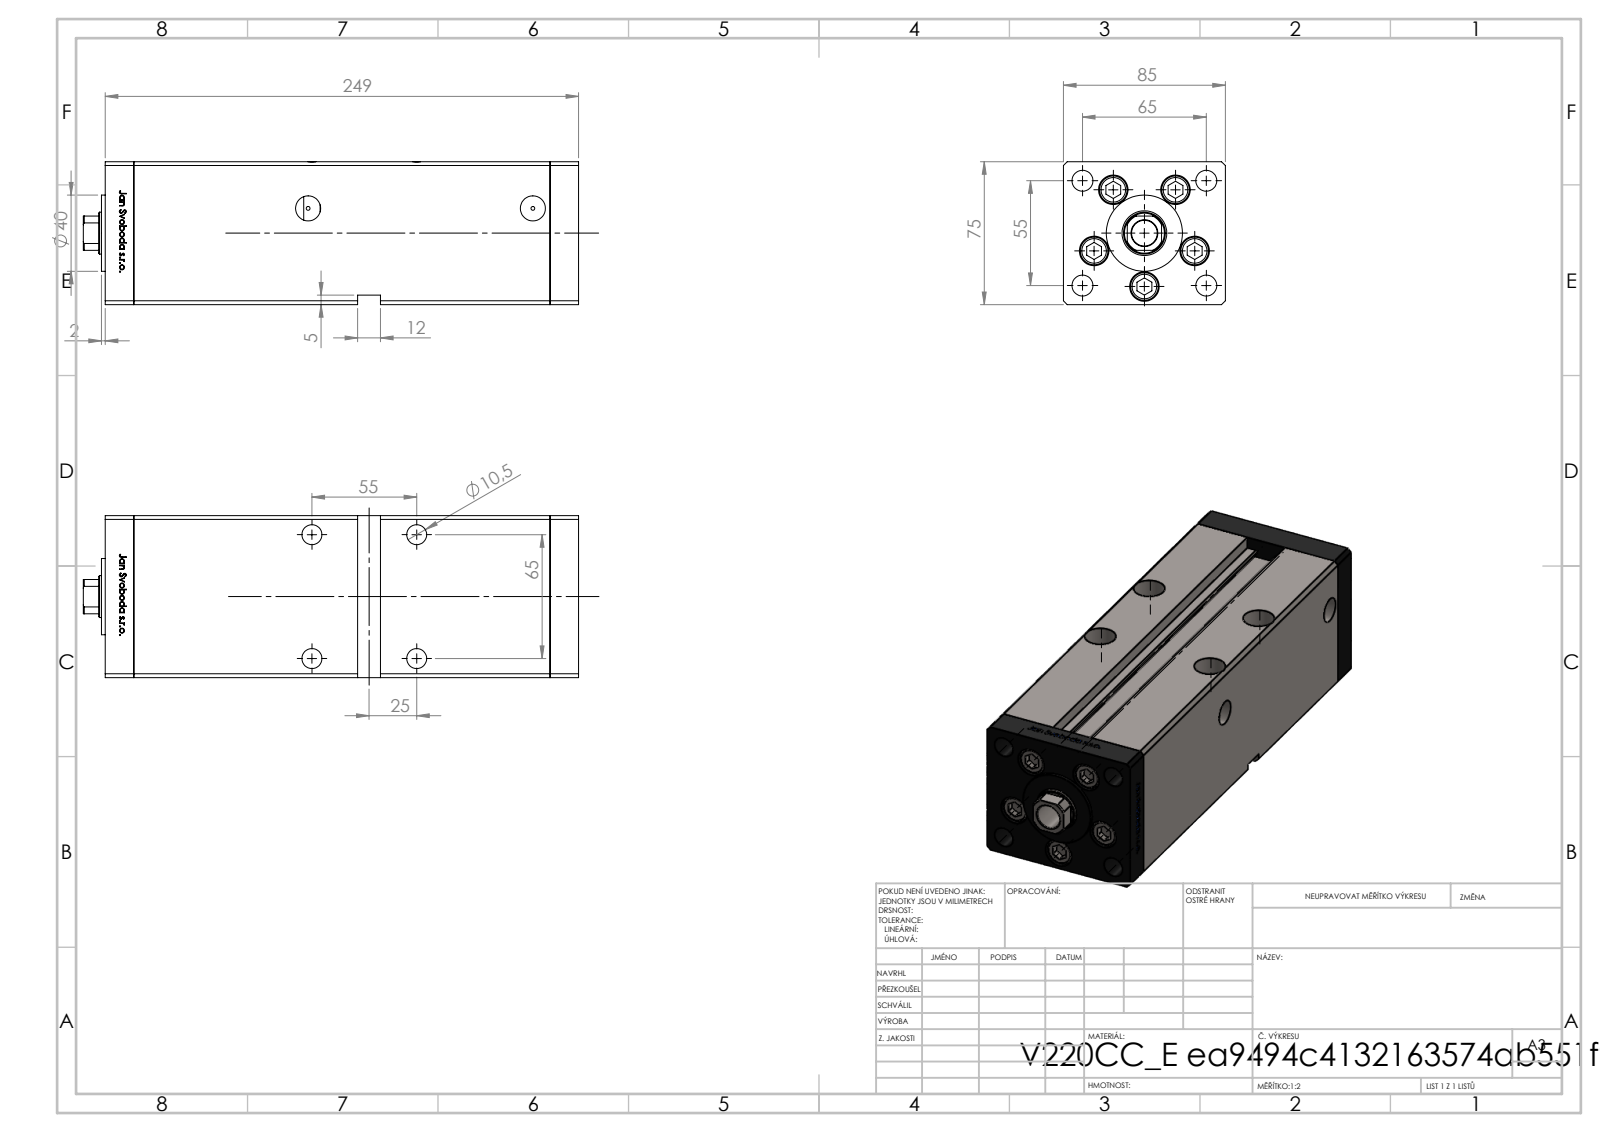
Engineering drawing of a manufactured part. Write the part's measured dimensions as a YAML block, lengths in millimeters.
part_name: "V220C_E MIDDLE; ALLEN BOLT; V220C_FRONT_E; V220C_VC_E (+1 more)"
step_written_by: "SolidWorks 2019 (CONFIG_CONTROL_DESIGN)"
units: millimeters
bodies: {solids: 14, faces: 1216, planar: 476, cylindrical: 166, other: 574}
overall_size: [260, 85, 75]
volume: 1342000
surface_area: 209040
round_holes:
  - {diameter: 11, count: 9}
  - {diameter: 15.5, count: 5}
  - {diameter: 10.5, count: 4}
  - {diameter: 16.5, count: 4}
  - {diameter: 2, count: 2}
  - {diameter: 13.16, count: 2}
  - {diameter: 13.5, count: 1}
  - {diameter: 22, count: 1}
  - {diameter: 23.5, count: 1}
round_bosses_or_shafts:
  - {diameter: 14.5, count: 5}
  - {diameter: 8, count: 5}
  - {diameter: 40, count: 1}
partial_cylinders:
  - {radius: 0.93, count: 2}
  - {radius: 10.5, count: 1}
face_to_face_distances: [85, 75, 15, 218.5, 233.5, 248.5, 10.5, 34.25, 68.5, 64.5]
hole_center_spacings: [28, 42.57, 55, 65, 85.15, 16.86, 19.17, 32.33]
